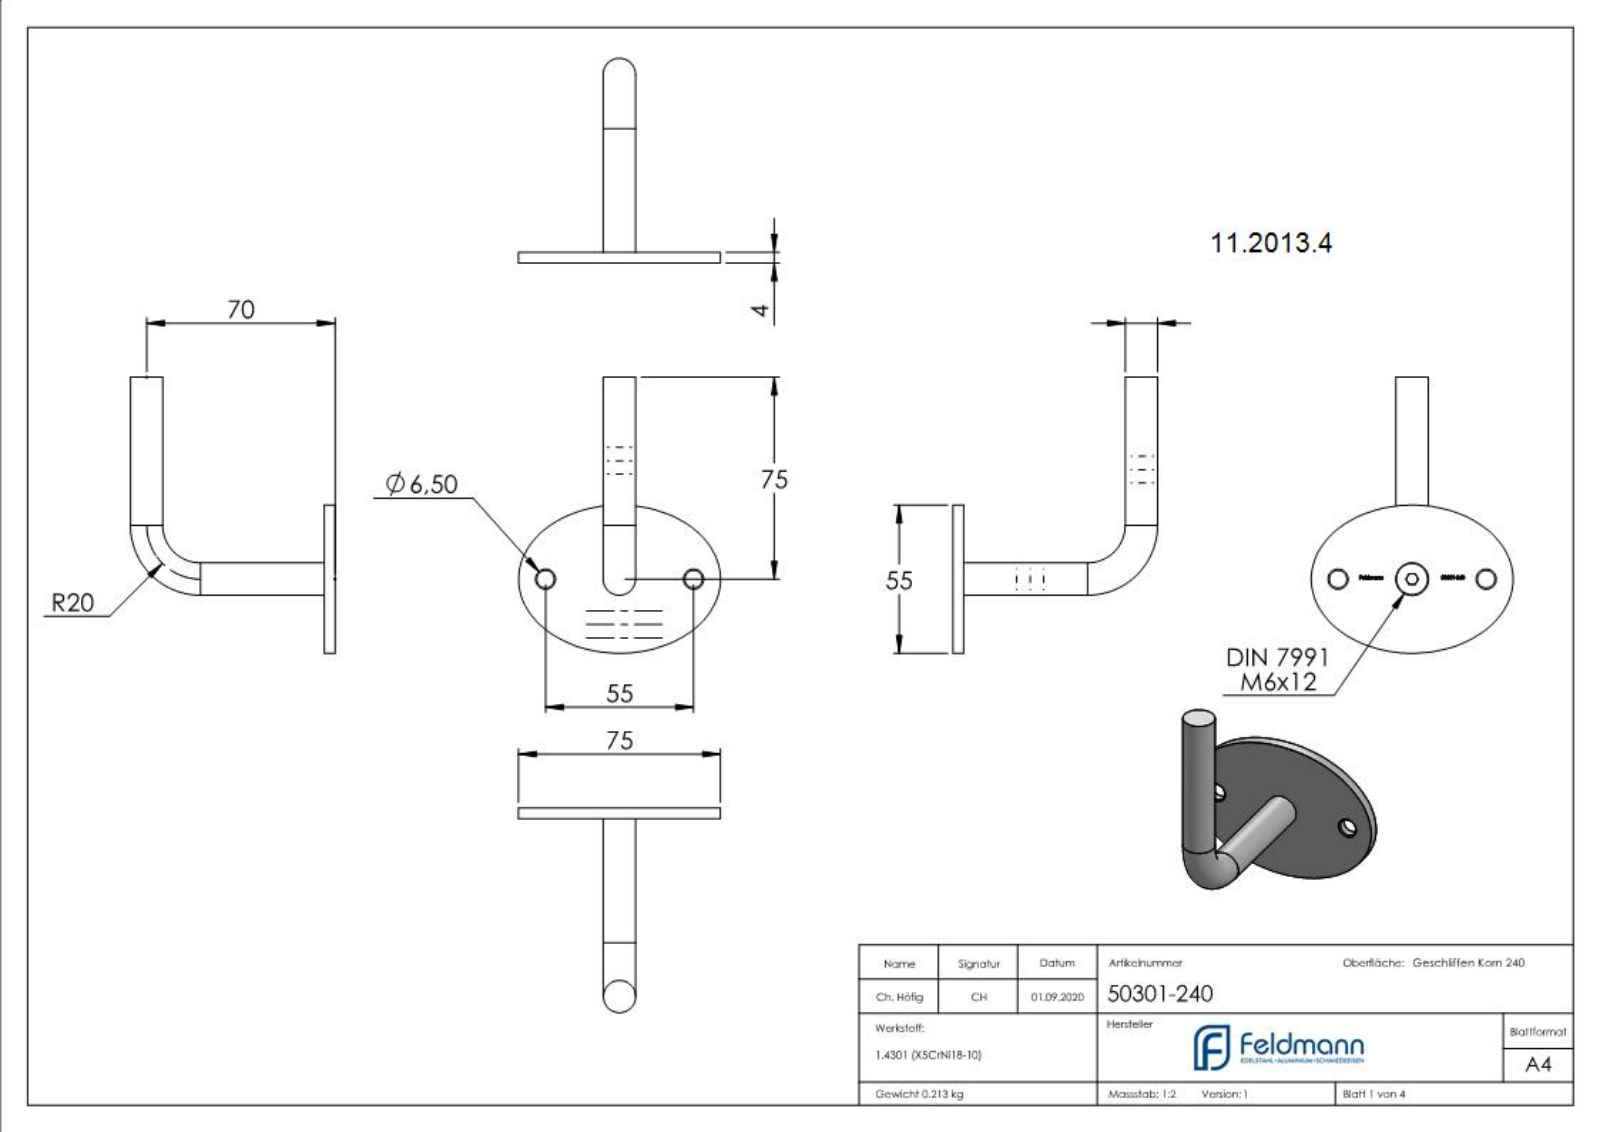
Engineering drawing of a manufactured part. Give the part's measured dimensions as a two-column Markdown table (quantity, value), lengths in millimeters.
| quantity | value |
| --- | --- |
| part name | 50301-240; socket countersunk head screw_din_DIN 7991 - M6 x 12 --- 5.7S; 50301-240 Teil2; 50301-240 Teil1_50301-240 Teil1 (+3 more) |
| STEP written by | SolidWorks 2018 (CONFIG_CONTROL_DESIGN) |
| units | millimeters |
| bodies | 3 solids, 317 faces (134 planar, 30 cylindrical, 153 other) |
| overall size | 102.5 × 76 × 75 |
| volume | 27 318 mm³ |
| surface area | 13 305 mm² |
| round holes (diameter × count) | 6.5 × 2, 5 × 1, 7 × 1, 12.2 × 1 |
| round bosses / shafts (diameter × count) | 12 × 2, 11.57 × 1, 6 × 1 |
| main face-to-face distances | 4, 1, 3, 13, 12, 9, 4.02, 72.99, 77.01, 0.9 |
| hole center spacings | 27.5, 55 |
